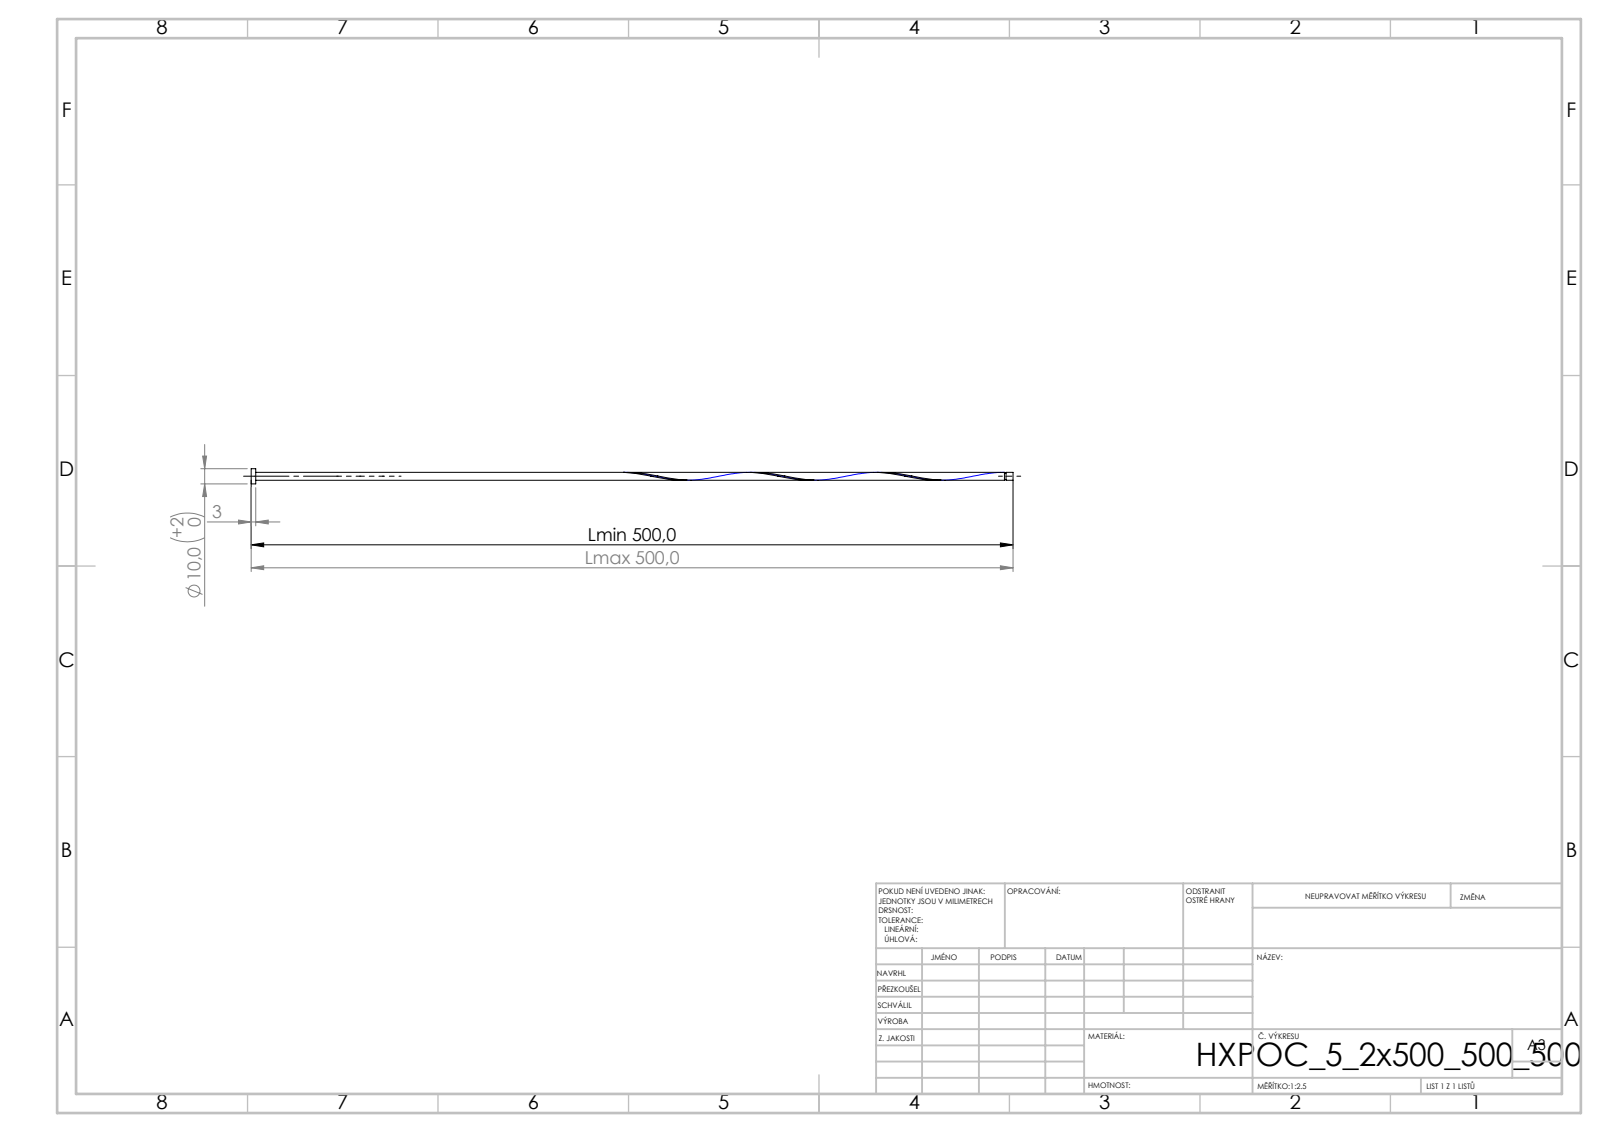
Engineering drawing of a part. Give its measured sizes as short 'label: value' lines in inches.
written by: SolidWorks 2019 (CONFIG_CONTROL_DESIGN)
unit: in
bodies: 1 solid, 16 faces (6 planar, 9 cylindrical, 1 other)
size: 19.685 × 0.394 × 0.394
volume: 0.796 in³; area: 17.41 in²
bosses: 1× ⌀0.394, 1× ⌀0.205, 1× ⌀0.164
face distances: 0.118, 19.685, 19.567, 19.505, 19.387, 0.18, 19.464, 19.346, 0.041, 0.221
